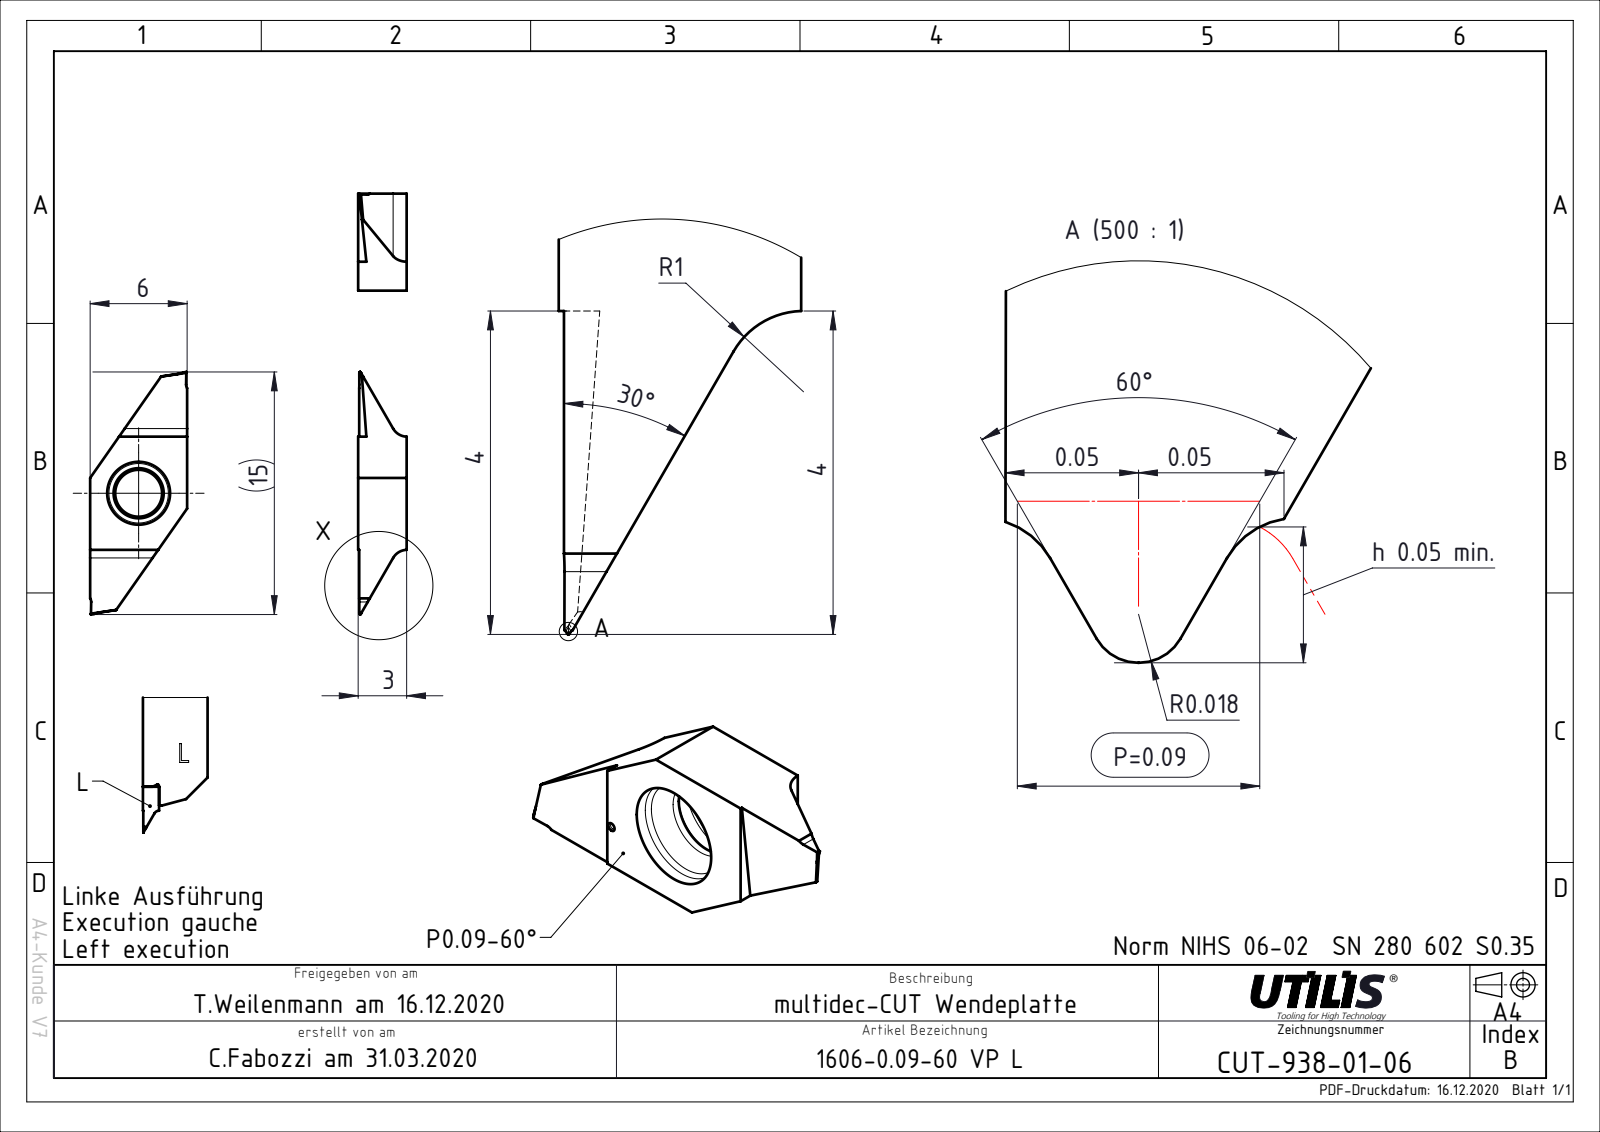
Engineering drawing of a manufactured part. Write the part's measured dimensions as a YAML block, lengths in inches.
part_name: "CUT-938-01; ASME Y14.5"
step_written_by: "FormatWorks Professional (AP242_MANAGED_MODEL_BASED_3D_ENGINEERING_MIM_LF)"
units: inches
bodies: {solids: 1, faces: 34, planar: 20, cylindrical: 14, other: 0}
overall_size: [0.591, 0.236, 0.118]
volume: 0.008
surface_area: 0.324
round_holes:
  - {diameter: 0.114, count: 1}
partial_cylinders:
  - {radius: 0.039, count: 2}
face_to_face_distances: [0.236, 0.118, 0.354, 0.276, 0.472, 0.283, 0.283]
